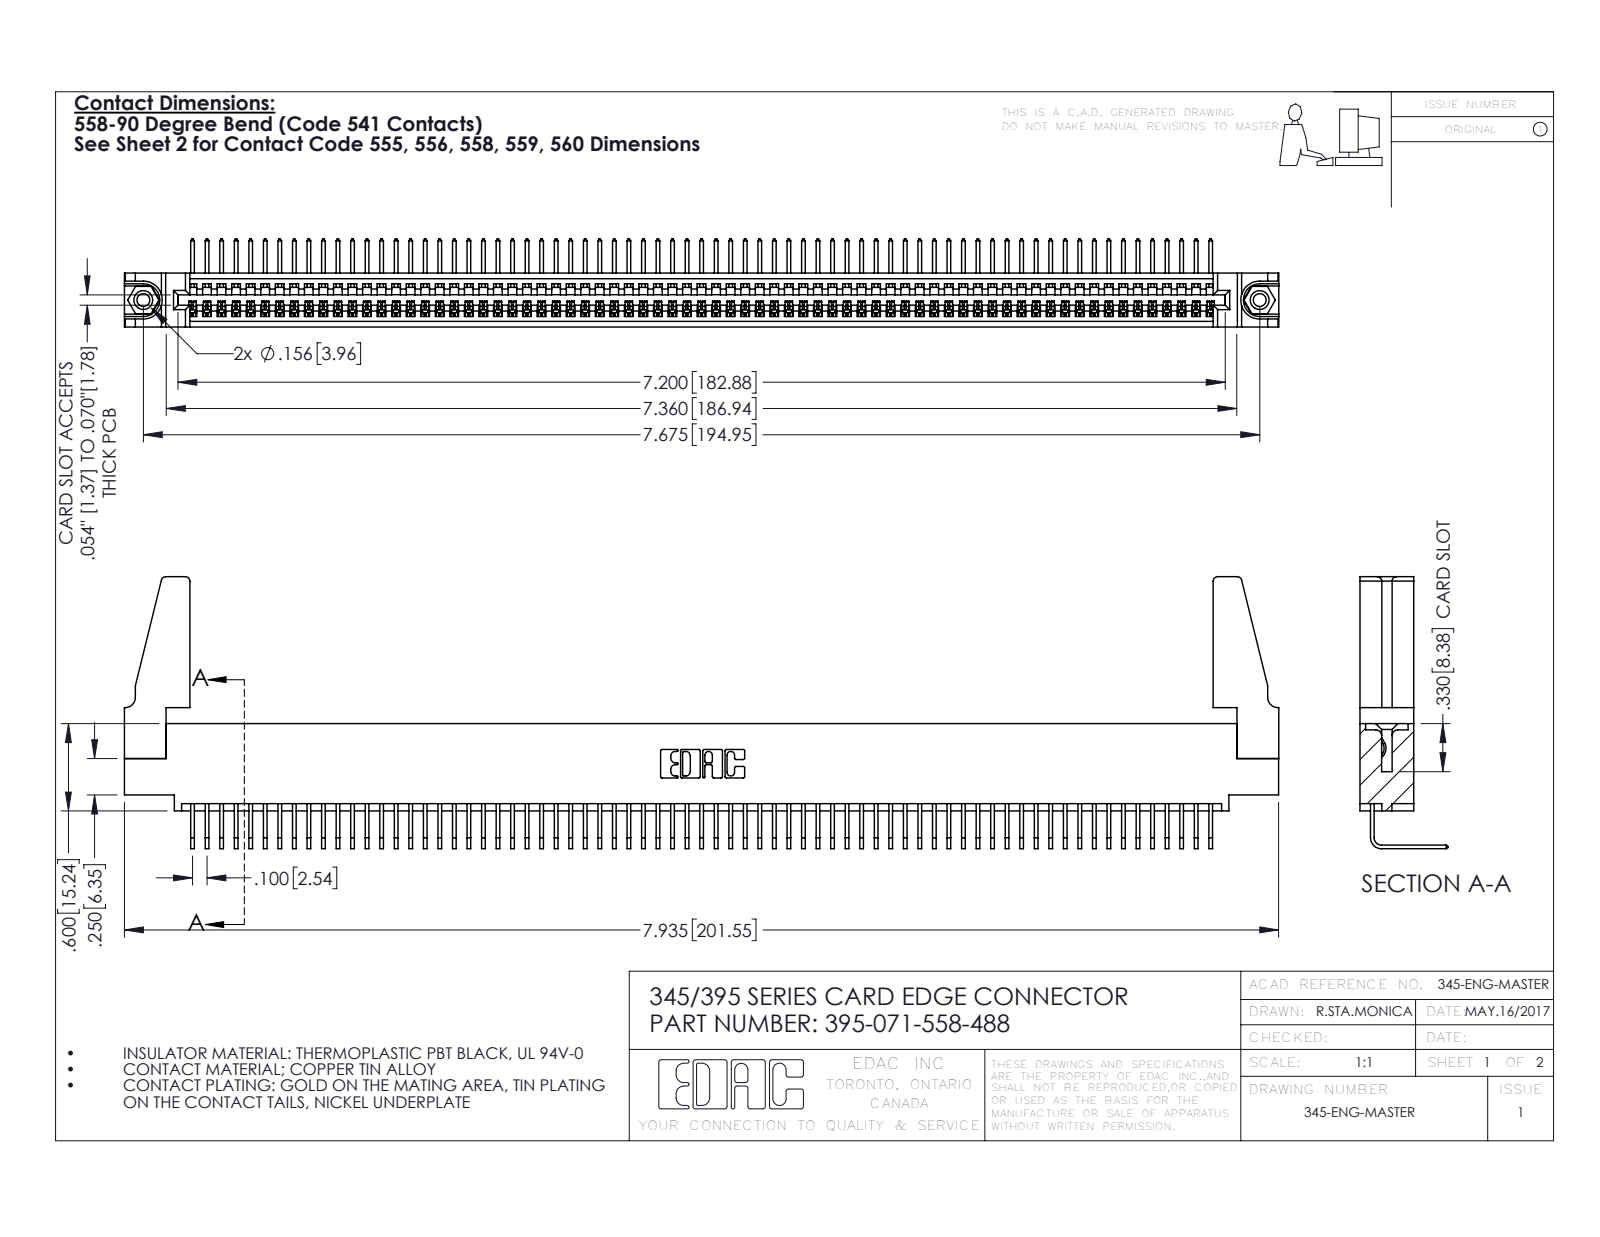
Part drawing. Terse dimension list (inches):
name: 395-071-558-488; 345-220-078_345-220-088; 345 Part_0.110 Offset - 0.156 Dia-TH; 345-292-001_558 Tail - 2 (+1 more)
written by: SolidWorks 2016 (CONFIG_CONTROL_DESIGN)
unit: in
bodies: 76 solids, 4514 faces (3138 planar, 1360 cylindrical, 16 other)
size: 7.936 × 1.869 × 0.605
volume: 1.391 in³; area: 48 in²
holes: 2× ⌀0.089, 2× ⌀0.125, 2× ⌀0.156, 1× ⌀0.064
bosses: 2× ⌀0.155
rounds: 142× R0.006, 22× R0.01, 8× R0.03, 6× R0.007, 6× R0.031, 3× R0.026, 2× R0.031, 2× R0.04
face distances: 0.072, 0.298, 0.37, 0.098, 0.272, 0.025, 0.2, 0.225, 0.149, 0.072
hole spacings: 0.27, 7.439, 7.675
